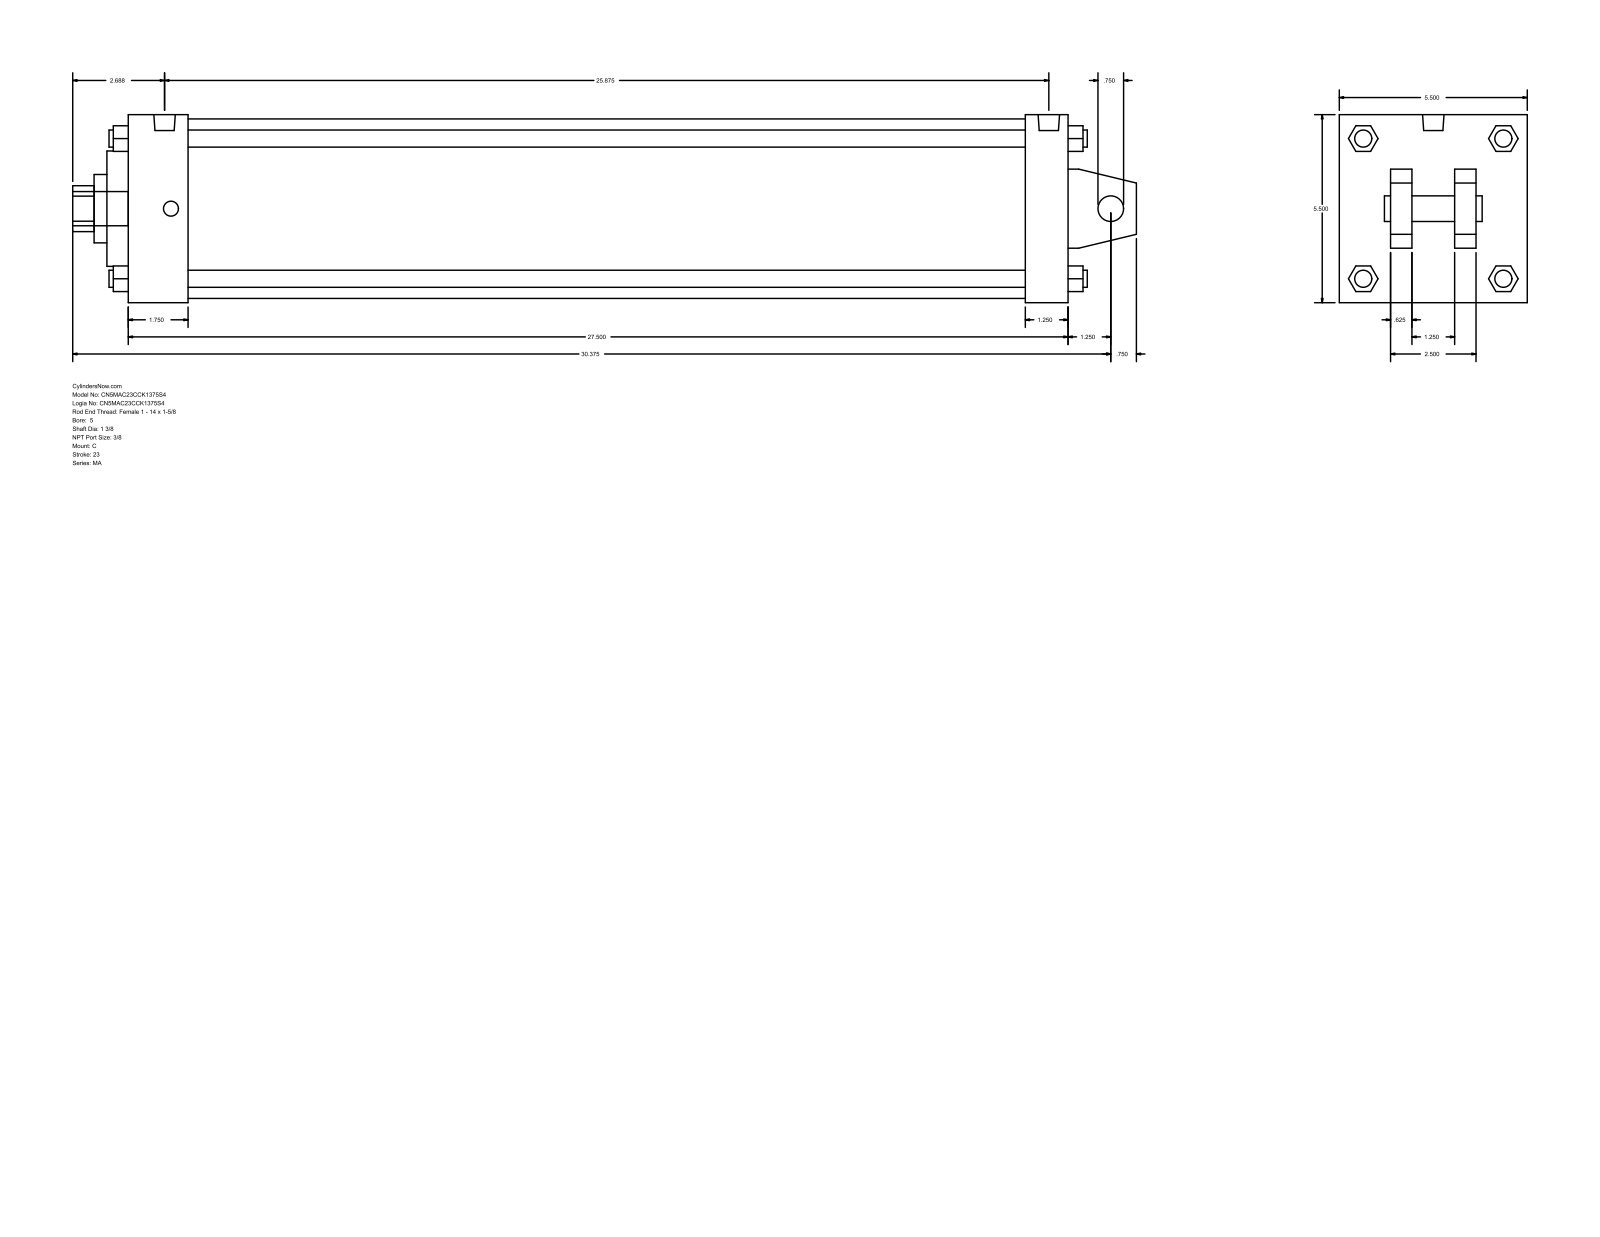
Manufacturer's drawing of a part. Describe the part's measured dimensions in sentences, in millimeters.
The part is named "MA_C__0500_1.375". Its 3-D file was written by "GSSL Pune (CONFIG_CONTROL_DESIGN)". It is 0 solids with 141 faces: 109 planar, 32 cylindrical and 0 other. Overall it measures 790.58 by 139.7 by 139.7 millimeters. Round holes: 1 of diameter 19.05, 1 of diameter 34.92, 1 of diameter 50.8, 1 of diameter 85.72, 1 of diameter 133.35. Round bosses or shafts: 4 of diameter 12.7, 4 of diameter 11.11, 2 of diameter 15.93, 1 of diameter 25.4. Partial cylindrical surfaces (rounded edges, fillets, slot ends): 1 of radius 17.06. The main face-to-face distances are 139.7, 698.5, 15.87, 666.75, 31.75, 44.45, 622.3, 654.05, 38.1, 101.6.
